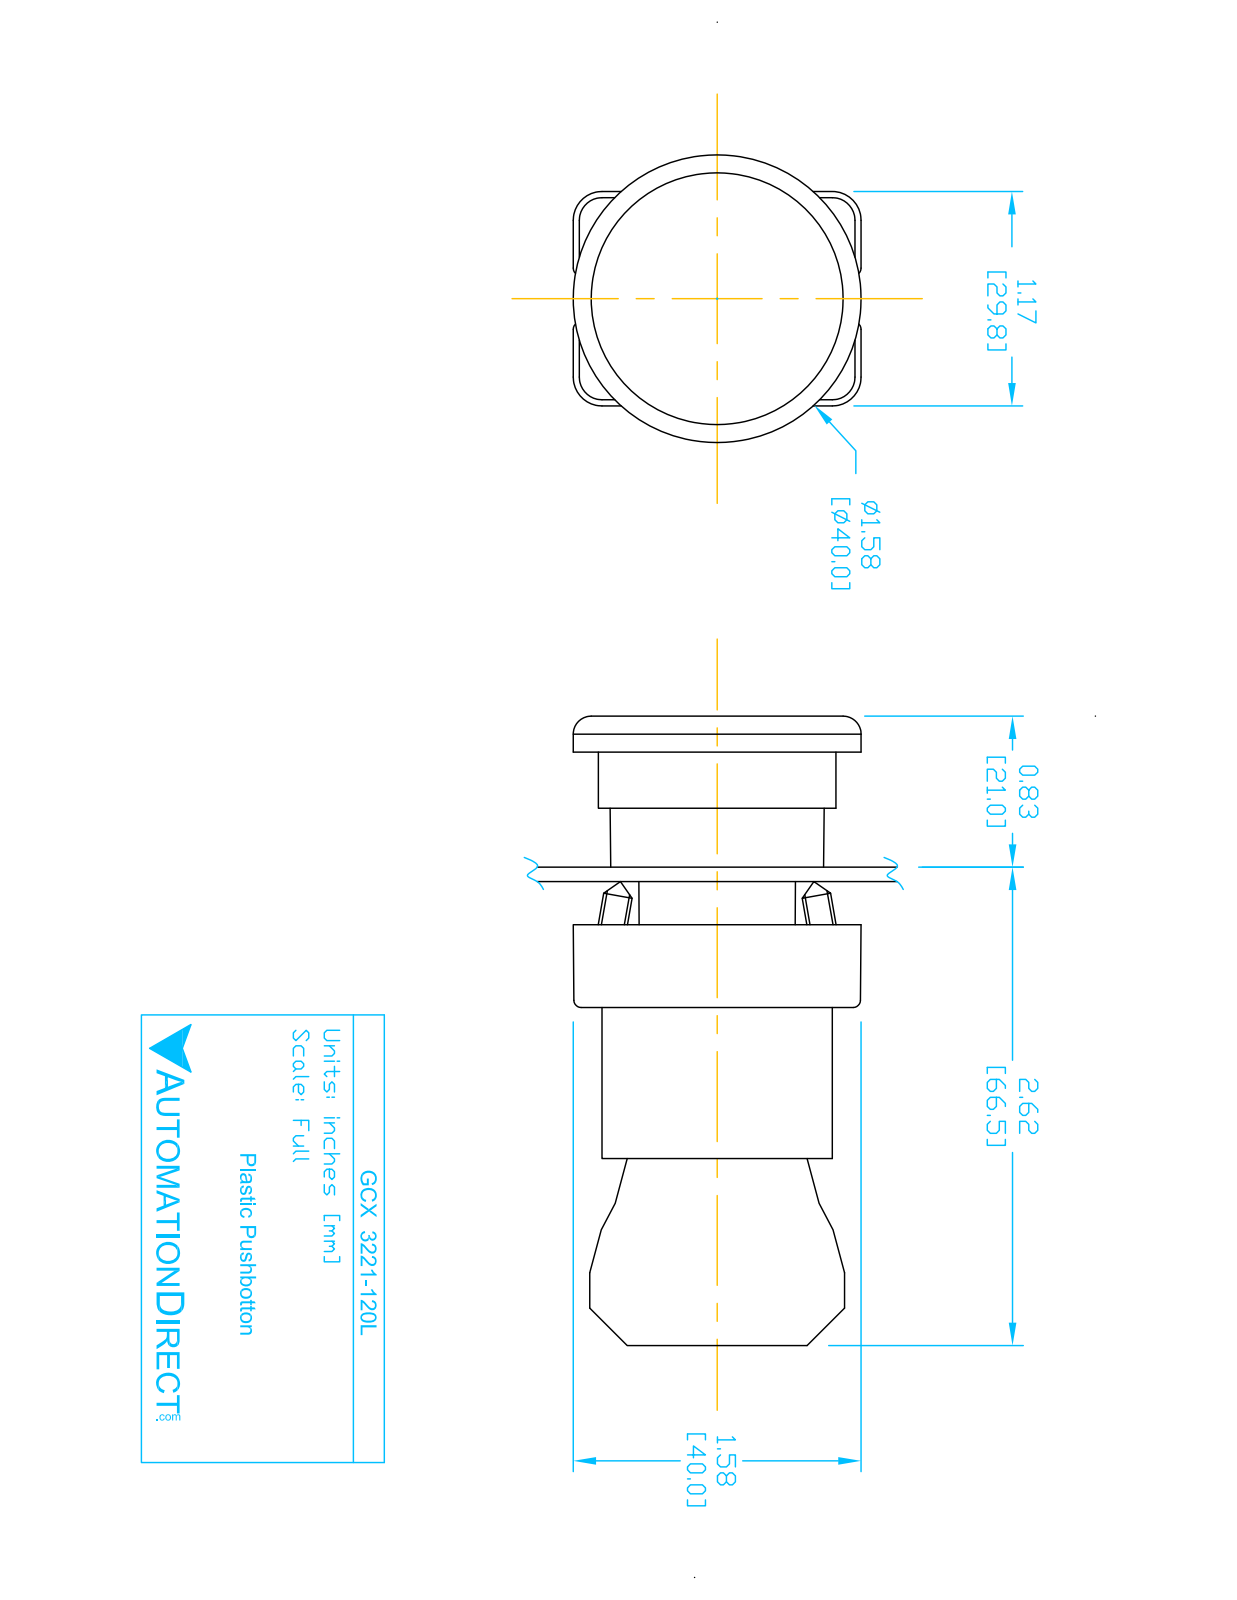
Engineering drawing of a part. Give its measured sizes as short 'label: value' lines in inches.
name: ECX3029-2; GCX322X OPERATOR; ecx1030; GCX3221-120L (+1 more)
written by: SolidWorks 2016 (AUTOMOTIVE_DESIGN)
unit: in
bodies: 7 solids, 431 faces (252 planar, 146 cylindrical, 33 other)
size: 3.469 × 1.581 × 1.575
volume: 2.895 in³; area: 40.89 in²
holes: 2× ⌀0.079, 2× ⌀0.124, 2× ⌀0.13, 1× ⌀0.087, 1× ⌀0.197, 1× ⌀0.469, 1× ⌀0.878, 1× ⌀0.888, 1× ⌀1.024, 1× ⌀1.181
bosses: 4× ⌀0.157, 1× ⌀1.299, 1× ⌀1.175, 1× ⌀0.945, 1× ⌀0.856, 1× ⌀0.78, 1× ⌀0.504
rounds: 24× R0.059, 12× R0.041, 12× R0.124, 12× R0.157, 8× R0.039, 2× R0.128, 1× R0.02, 1× R0.063
face distances: 0.827, 2.445, 1.618, 0.579, 2.287, 1.461, 0.157, 0.587, 0.031, 1.165
hole spacings: 0.236, 0.539, 0.472, 0.484
